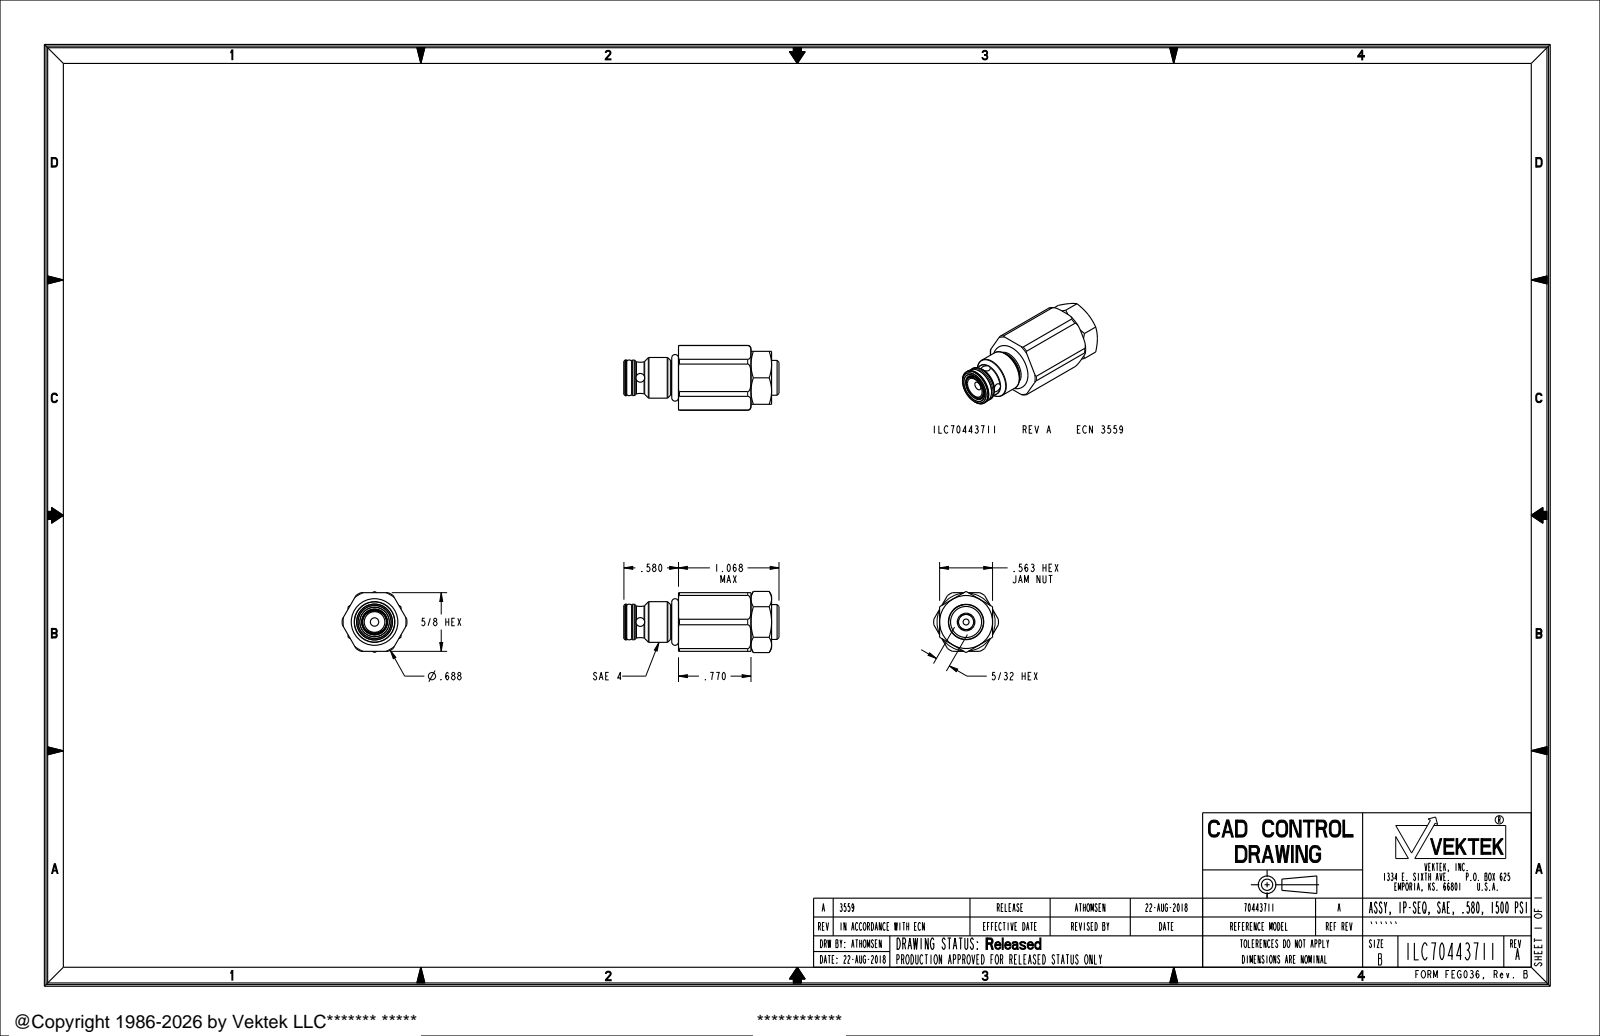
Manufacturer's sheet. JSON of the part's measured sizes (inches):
{"part_name": "ILC70443711", "step_written_by": "PRO/ENGINEER BY PARAMETRIC TECHNOLOGY CORPORATION, 2013320 (AUTOMOTIVE_DESIGN)", "units": "inches", "bodies": {"solids": 1, "faces": 214, "planar": 45, "cylindrical": 69, "other": 100}, "overall_size": [1.648, 0.688, 0.65], "volume_in3": 0.386, "surface_area_in2": 4.536, "round_holes": [[0.093, 2], [0.161, 1], [0.247, 1], [0.27, 1], [0.375, 1], [0.5, 1], [0.528, 1]], "round_bosses_or_shafts": [[0.432, 1], [0.382, 1], [0.377, 1], [0.37, 1], [0.364, 1], [0.344, 1], [0.236, 1]], "partial_cylinders_radius": [[0.115, 2], [0.094, 1], [0.344, 1]], "face_to_face_distances": [0.623, 0.562, 0.77, 0.219, 0.989, 0.052, 0.27, 0.718, 0.079, 0.298]}
